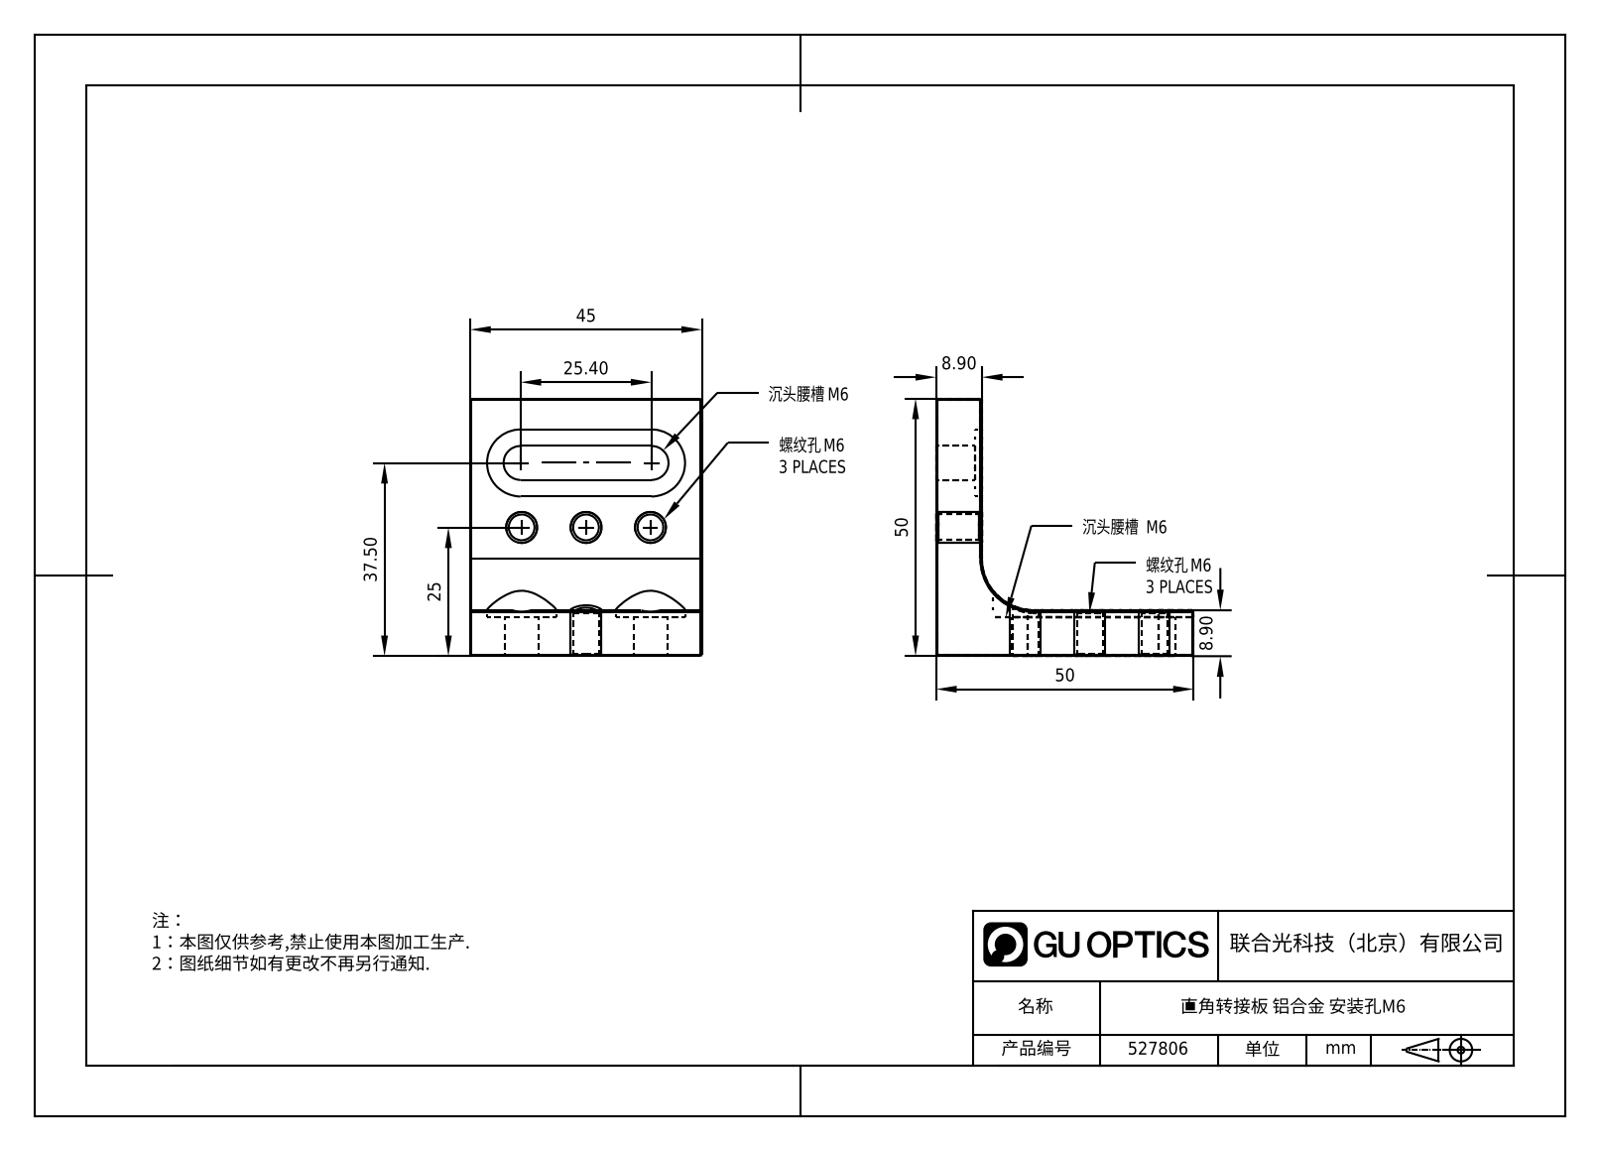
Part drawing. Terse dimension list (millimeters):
name: 7.5.4.6-MCS-50C
written by: SolidWorks 2021 (CONFIG_CONTROL_DESIGN)
unit: mm
bodies: 1 solid, 108 faces (52 planar, 31 cylindrical, 25 other)
size: 50 × 50 × 45
volume: 29 648 mm³; area: 11 774 mm²
holes: 6× ⌀5
rounds: 6× R3.3, 4× R6.75, 2× R6.5, 1× R10
face distances: 8.9, 7.5, 45, 1.4, 50, 41.1, 42.5, 6.6, 25, 6.7
hole spacings: 12.5, 25
